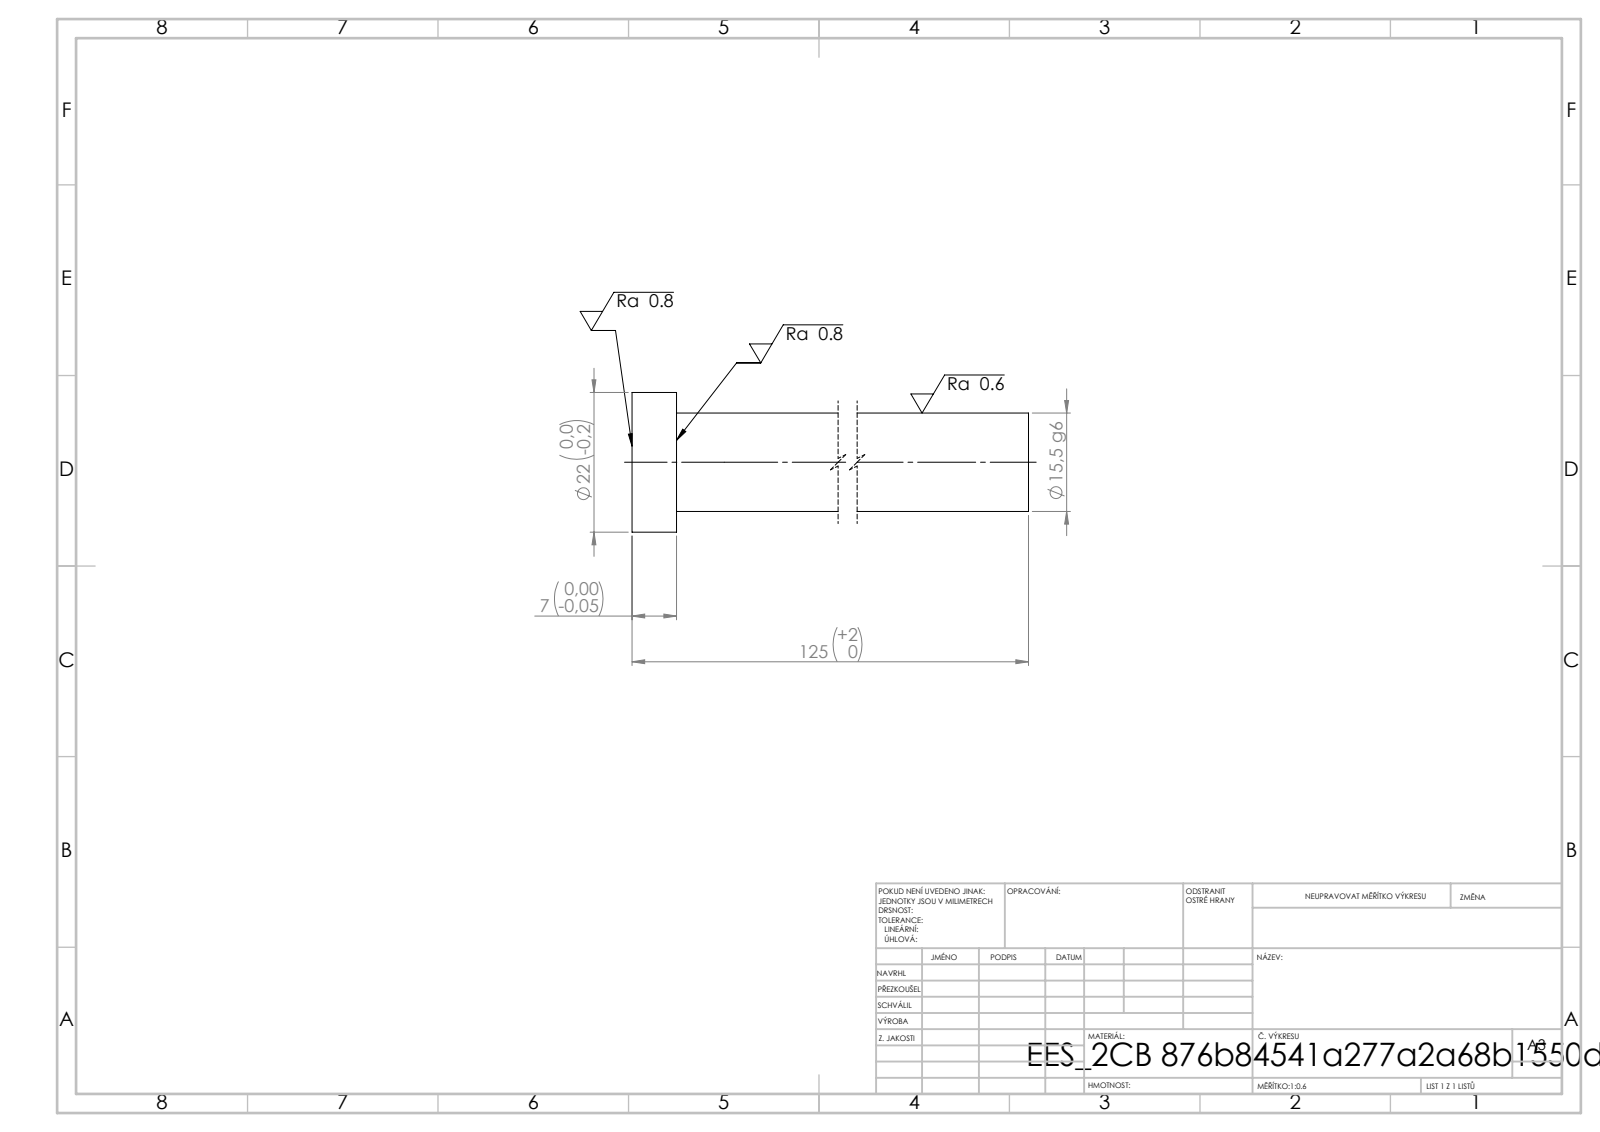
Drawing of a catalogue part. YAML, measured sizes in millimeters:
step_written_by: "SolidWorks 2019 (CONFIG_CONTROL_DESIGN)"
units: millimeters
bodies: {solids: 1, faces: 7, planar: 3, cylindrical: 4, other: 0}
overall_size: [125, 22, 22]
volume: 24927
surface_area: 6990
round_bosses_or_shafts:
  - {diameter: 22, count: 1}
  - {diameter: 15.5, count: 1}
face_to_face_distances: [7, 125, 118]
